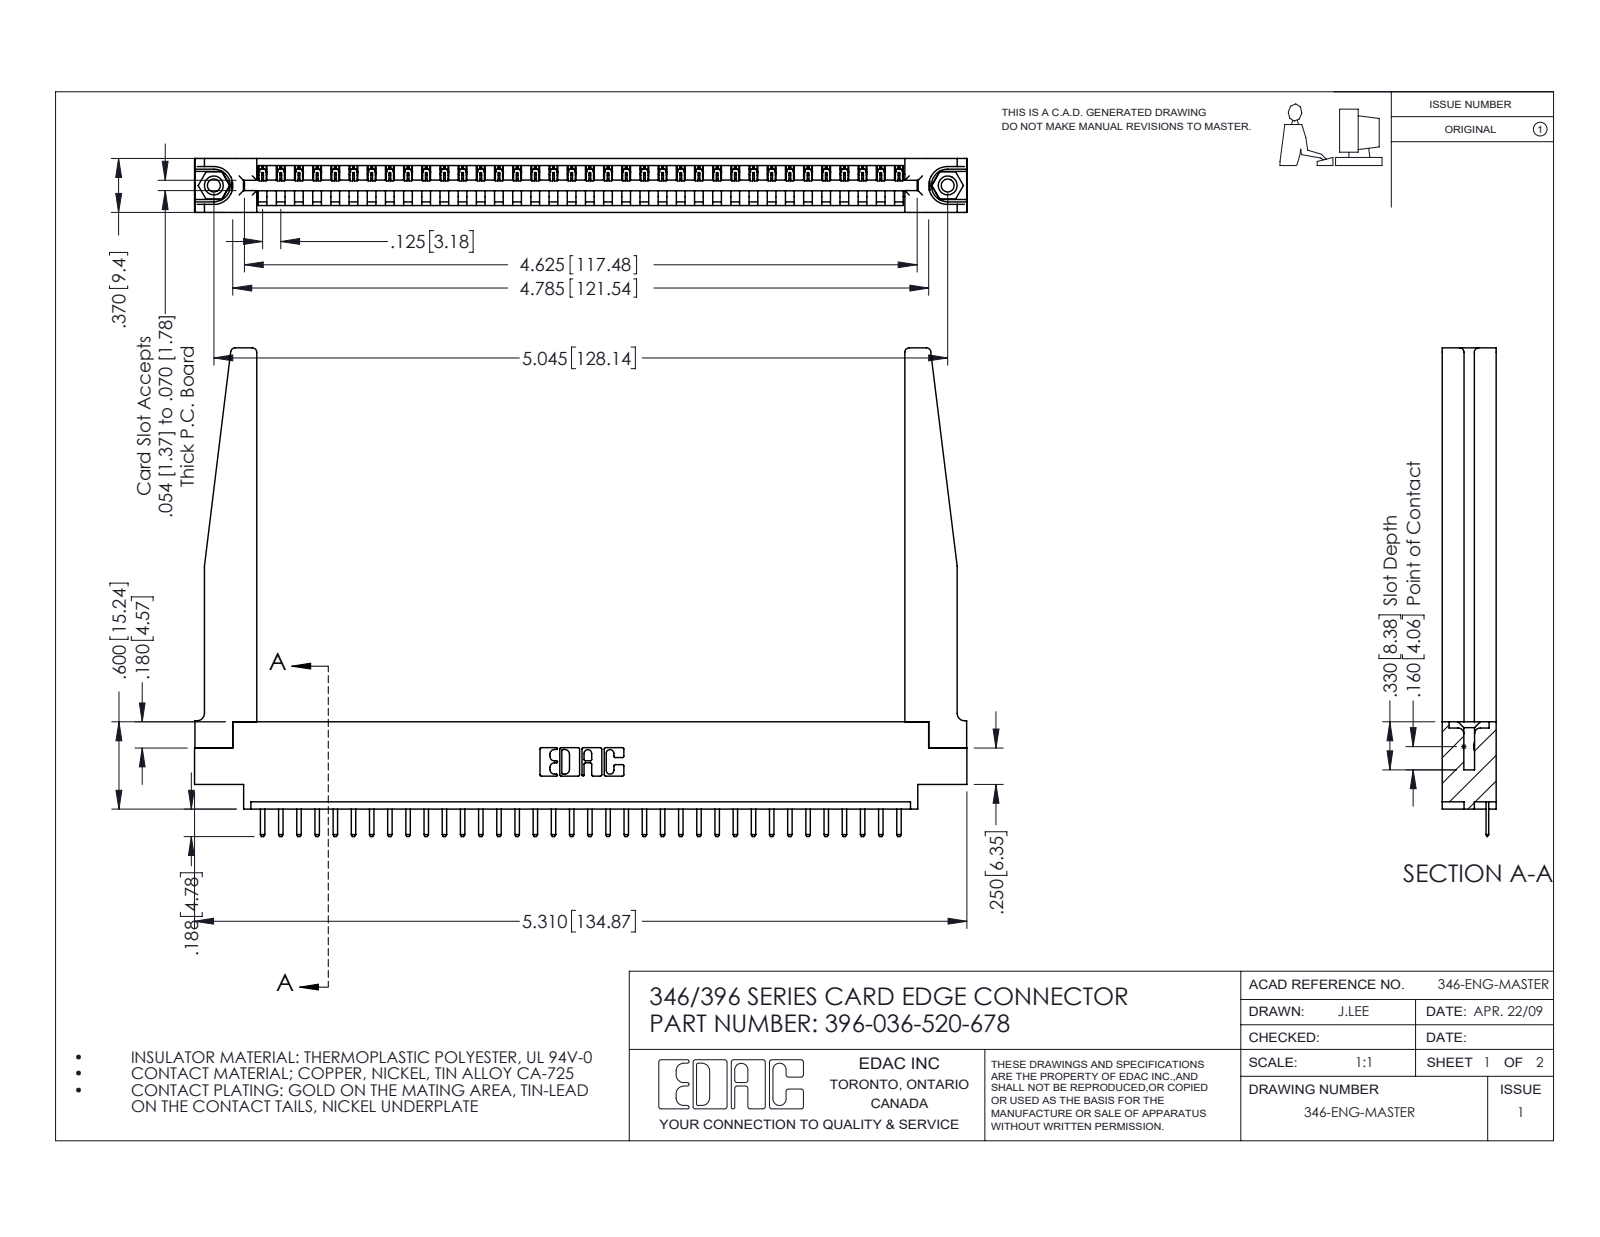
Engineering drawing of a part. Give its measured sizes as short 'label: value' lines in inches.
name: 345-292-001_345-293-120; 346 Part_0.170 Offset - 0.156 Dia-TH; 346-220-078_345-220-078; 345-250-001_345-250-001-102 (+1 more)
written by: SolidWorks 2016 (CONFIG_CONTROL_DESIGN)
unit: in
bodies: 41 solids, 2592 faces (1734 planar, 806 cylindrical, 52 other)
size: 5.31 × 3.358 × 0.37
volume: 1.191 in³; area: 34.18 in²
holes: 2× ⌀0.089, 2× ⌀0.125, 2× ⌀0.156, 1× ⌀0.064
bosses: 2× ⌀0.155
rounds: 74× R0.01, 72× R0.006, 22× R0.01, 8× R0.03, 6× R0.007, 6× R0.031, 3× R0.026, 2× R0.031
face distances: 0.37, 0.048, 0.322, 0.148, 0.072, 0.15, 0.25, 0.222, 0.1, 0.174
hole spacings: 0.246, 4.836, 5.045
